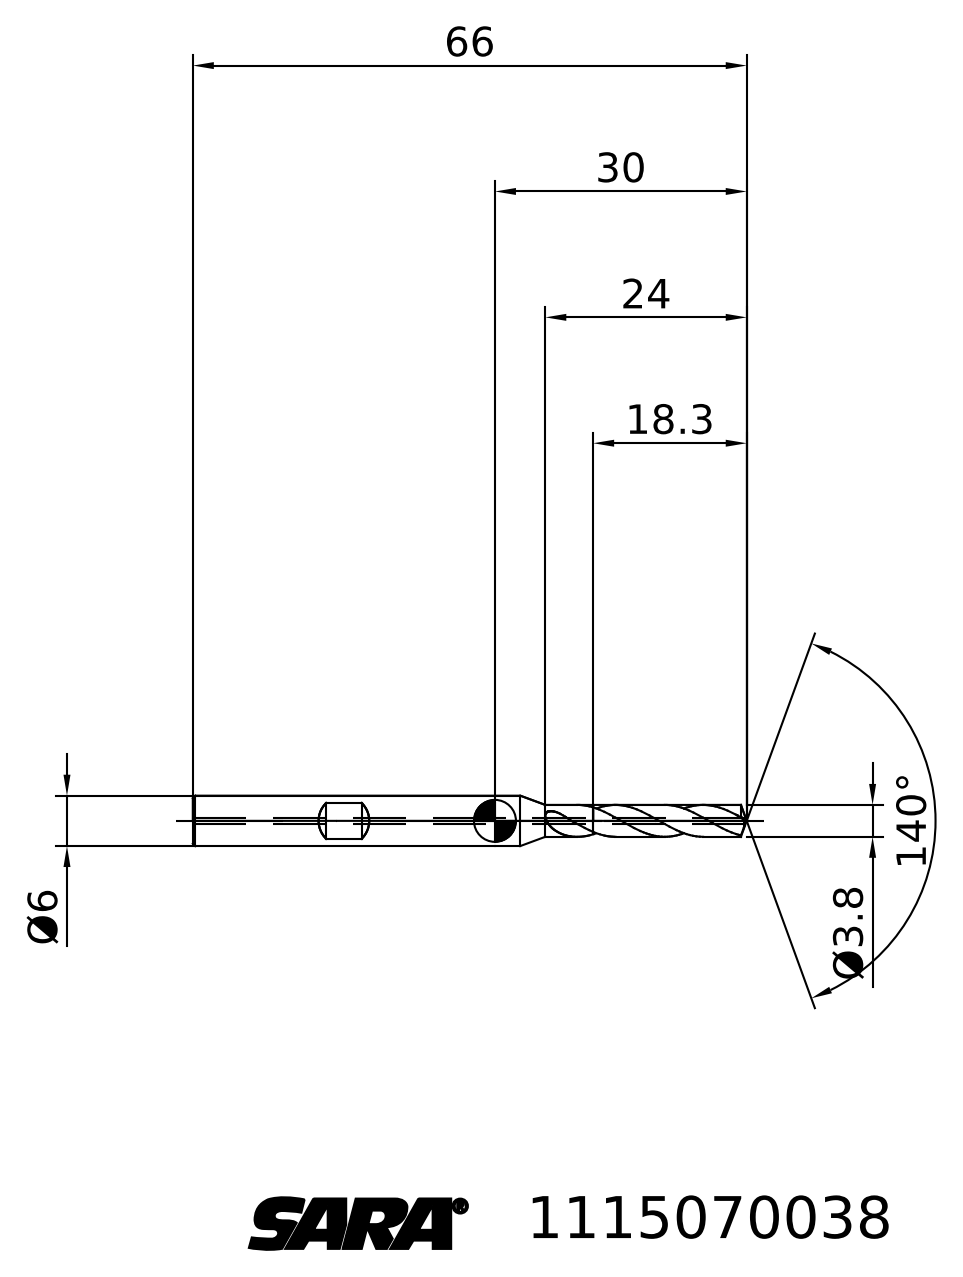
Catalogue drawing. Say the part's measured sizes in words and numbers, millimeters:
Its 3-D file was written by "TDM (AUTOMOTIVE_DESIGN)". It is 2 solids with 29 faces: 6 planar, 0 cylindrical and 23 other. Overall it measures 66 by 8.24 by 6 millimeters. Its volume is 1 326 cubic millimeters and its surface area 1 137 square millimeters. The main face-to-face distances are 47.7.
